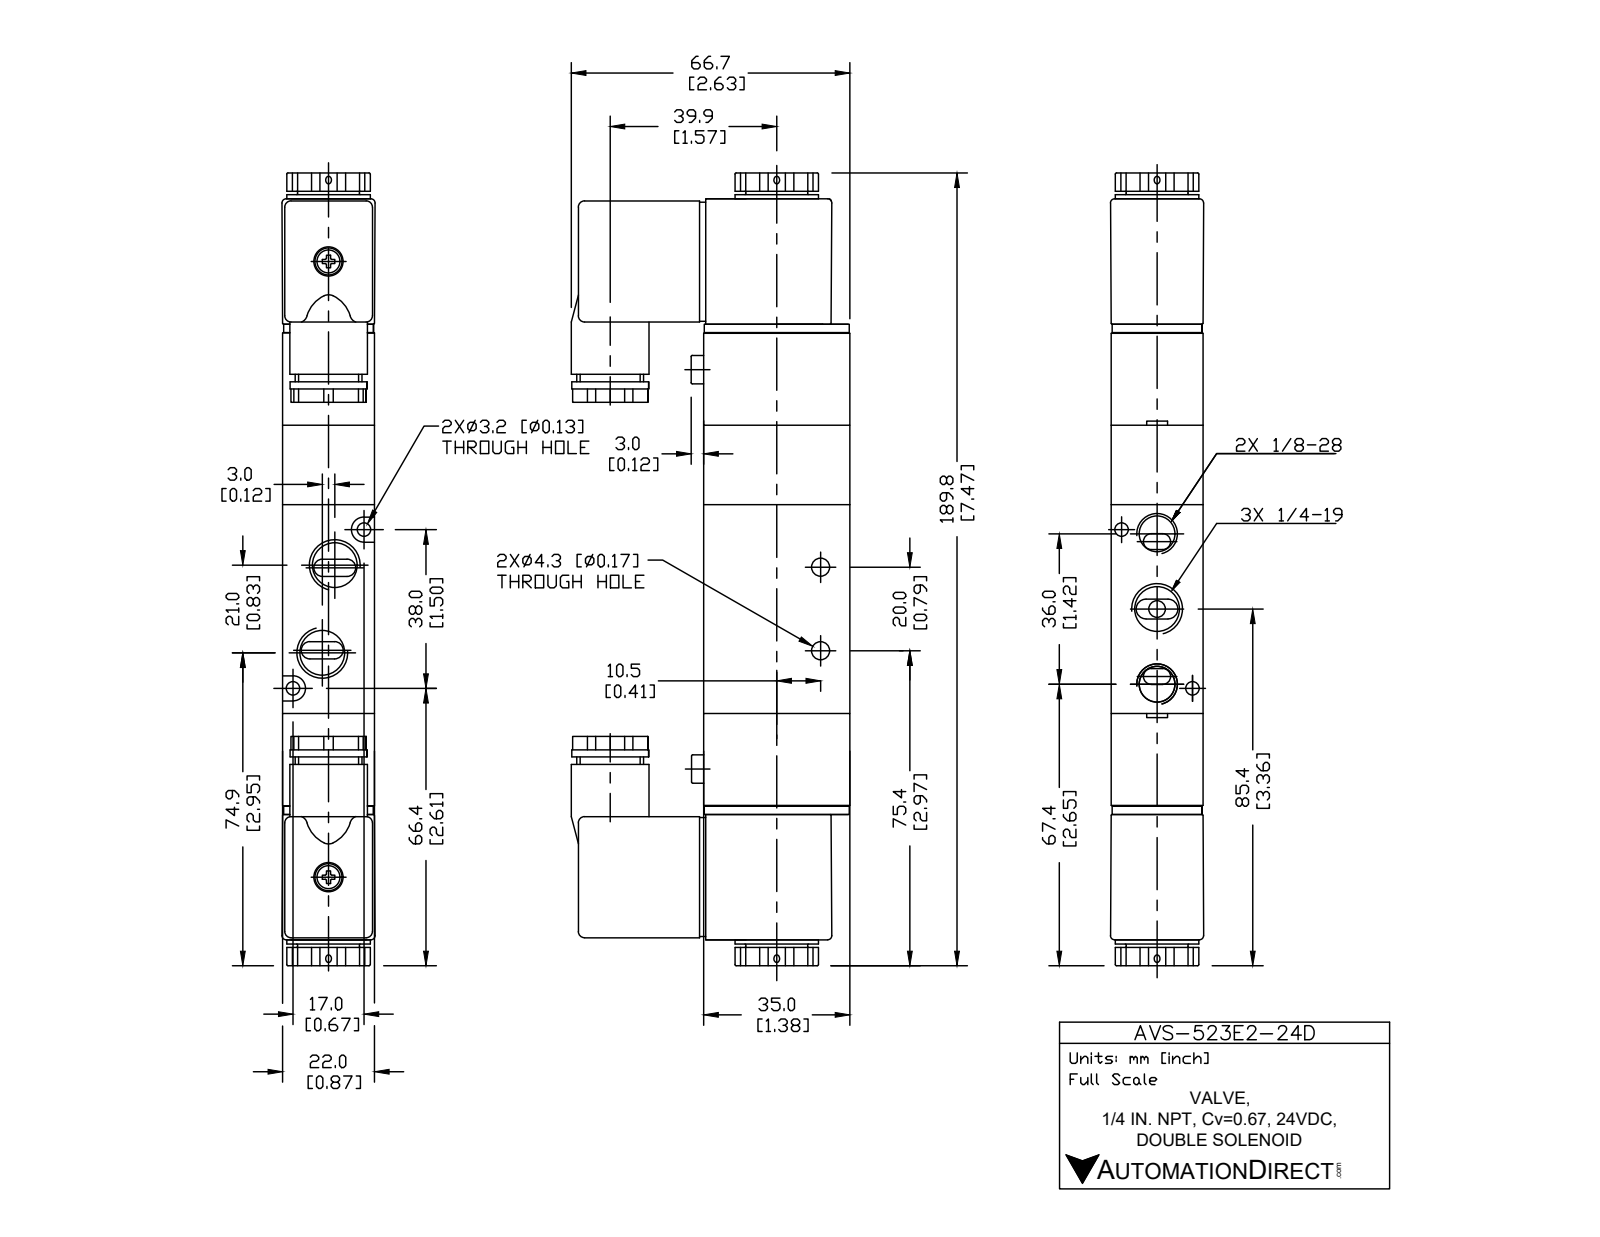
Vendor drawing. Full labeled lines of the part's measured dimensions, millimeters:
Part name (STEP PRODUCT): AVS-523E2-24D
STEP written by: SolidWorks 2015 (CONFIG_CONTROL_DESIGN)
Units: millimetres
Bodies: 5 solids, 236 faces (129 planar, 91 cylindrical, 16 other)
Overall size (bounding box): 189.82 × 66.7 × 22
Volume: 148 738 mm³ · Surface area: 37 934 mm²
Round holes (diameter × count): ⌀11.13 ×3, ⌀3.2 ×2, ⌀4.3 ×2, ⌀8.43 ×2, ⌀9.3 ×1
Round bosses / shafts (diameter × count): ⌀6.8 ×2, ⌀18.6 ×1, ⌀17.6 ×1, ⌀15.81 ×1, ⌀13.02 ×1, ⌀11 ×1
Partial cylindrical surfaces — rounded edges, fillets, slot ends (radius × count): R1.54 ×10, R0.3 ×8, R0.5 ×8, R1 ×8, R3 ×2
Main face-to-face distances: 0.88, 21.74, 1.95, 20.05, 22, 18.1, 22.62, 69, 30.59, 5.03
Hole centre spacings: 8.56, 18, 20.81, 37.96, 7.54, 7.83, 10.53, 10.55
